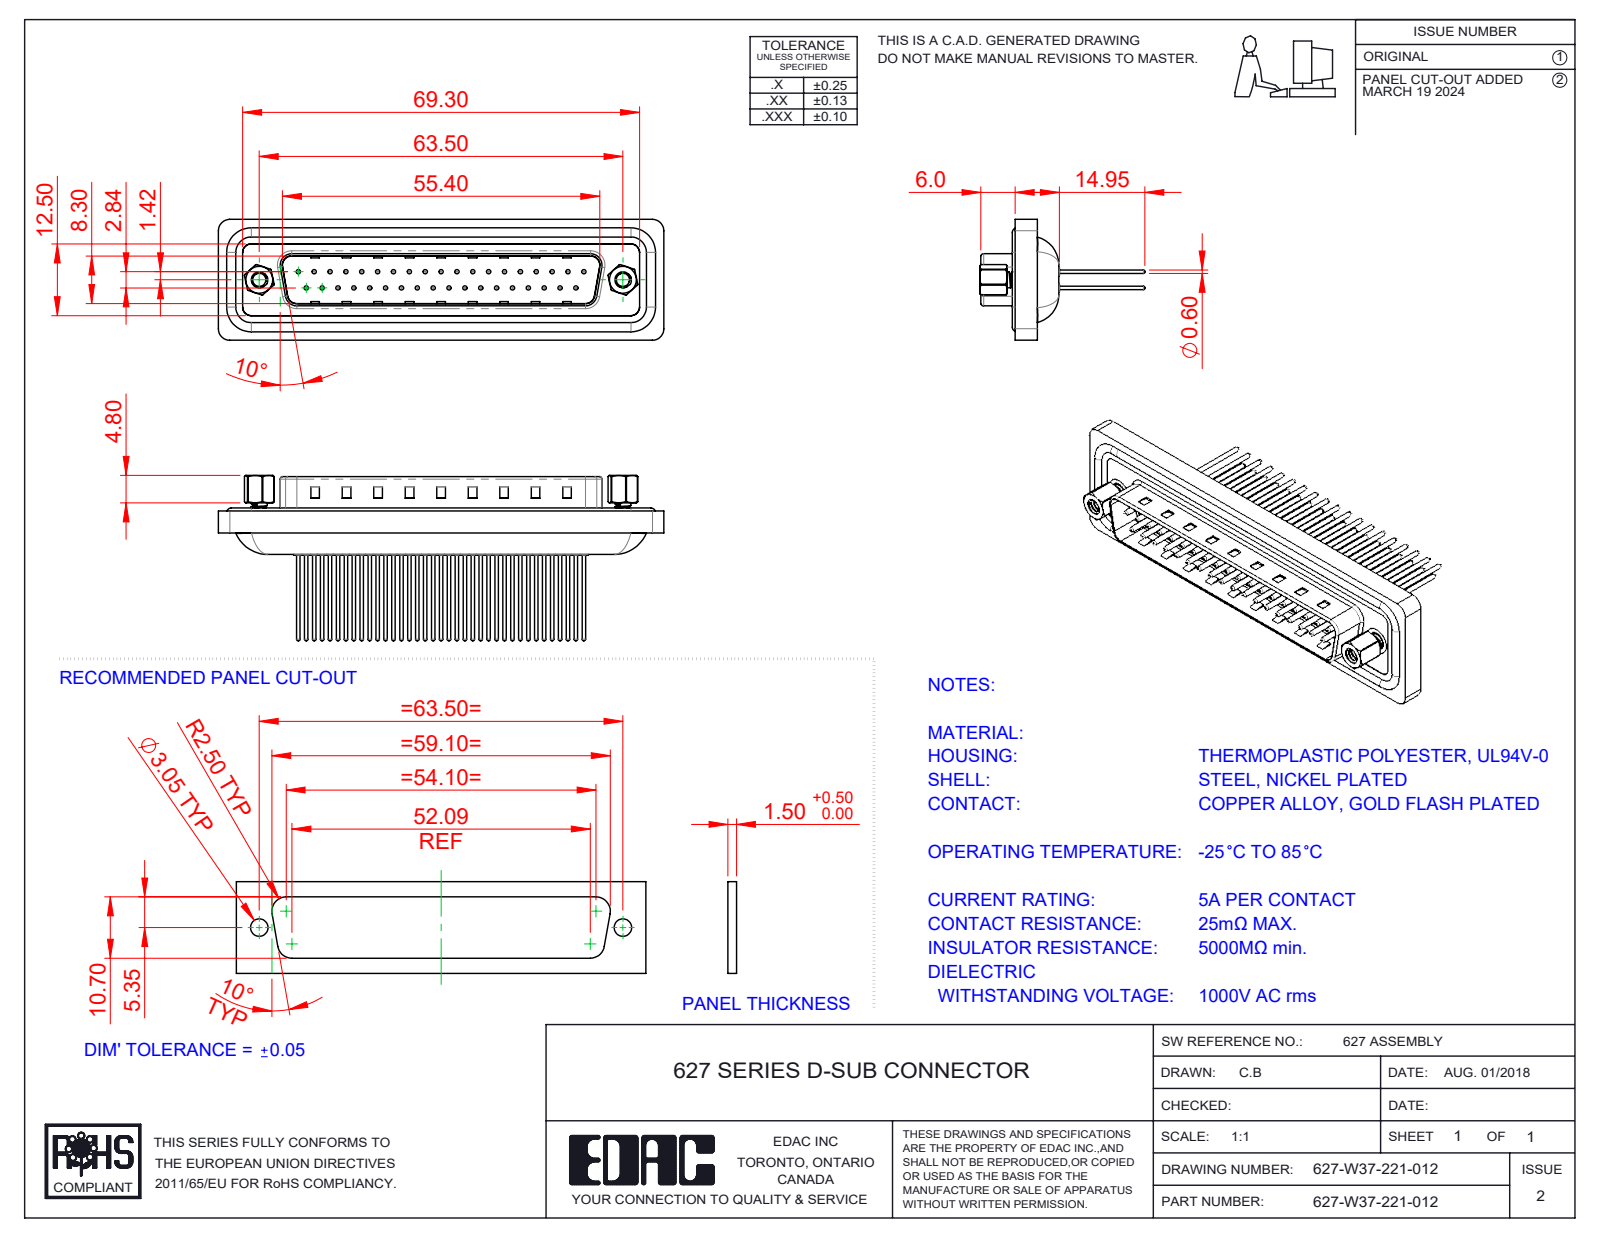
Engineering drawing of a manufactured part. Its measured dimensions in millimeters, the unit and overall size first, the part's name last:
Units: millimetres
Overall size (bounding box): 77.8 × 28.85 × 21.1
Round holes (diameter × count): ⌀0.75 ×37, ⌀1.5 ×37, ⌀1.6 ×37, ⌀2 ×37, ⌀2.26 ×2, ⌀2.29 ×2, ⌀4 ×2, ⌀4.8 ×2, ⌀5 ×2
Round bosses / shafts (diameter × count): ⌀0.6 ×37, ⌀1.5 ×9, ⌀1.6 ×4, ⌀4.9 ×2, ⌀2.79 ×2
Partial cylindrical surfaces — rounded edges, fillets, slot ends (radius × count): R2 ×16, R1.5 ×14, R0.5 ×8, R2.7 ×6, R0.9 ×4, R1.6 ×4, R4.3 ×4, R0.4 ×2
Main face-to-face distances: 0.75, 0.4, 4.1, 1.1, 2.75, 4.6, 3.75, 5.65, 15.45, 14.7
Hole centre spacings: 3.16, 2.77, 5.54, 8.31, 5.04, 10.1, 11.08, 12.78
Volume: 9 678 mm³ · Surface area: 15 182 mm²
Bodies: 45 solids, 1999 faces (496 planar, 816 cylindrical, 687 other)
Part name (STEP PRODUCT): 627W Waterproof Housing_37 Contacts; 627-W37-221-012; 627W Contact Row 2_21; 627W Housing_37 Contacts (+4 more)
STEP written by: SolidWorks 2023 (CONFIG_CONTROL_DESIGN)
